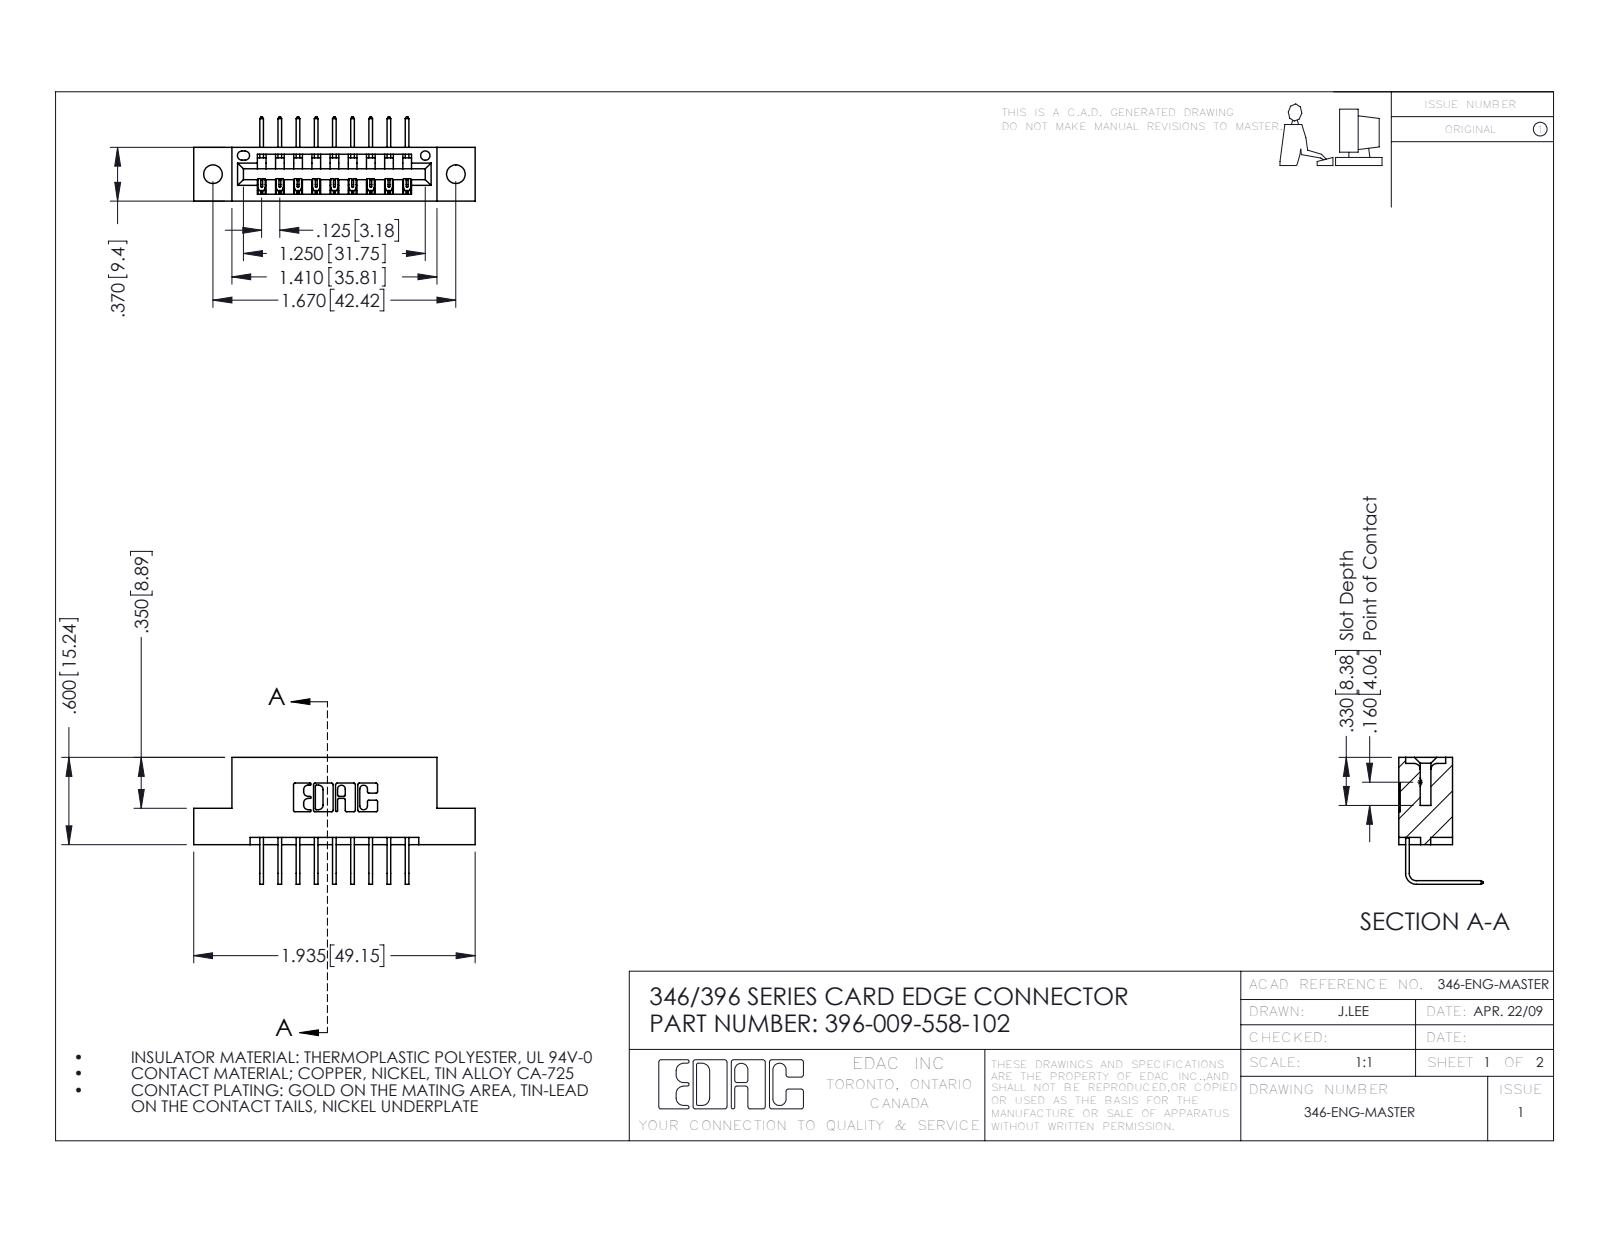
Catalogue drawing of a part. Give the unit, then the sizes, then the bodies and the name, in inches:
Units: inches
Overall size (bounding box): 1.935 × 0.873 × 0.58
Round holes (diameter × count): ⌀0.128 ×2, ⌀0.064 ×1
Partial cylindrical surfaces — rounded edges, fillets, slot ends (radius × count): R0.01 ×22, R0.006 ×18, R0.007 ×6, R0.031 ×6, R0.026 ×3, R0.031 ×2, R0.04 ×2, R0.014 ×1
Main face-to-face distances: 0.25, 0.322, 0.37, 0.048, 0.298, 0.025, 0.148, 0.222, 0.1, 0.174
Hole centre spacings: 0.246, 1.465, 1.67
Volume: 0.273 in³ · Surface area: 7.966 in²
Bodies: 10 solids, 662 faces (454 planar, 208 cylindrical, 0 other)
Part name (STEP PRODUCT): 346 Part_Flush Mounting Lugs - 0.128 Dia; 345-292-001_558 Tail - 2; 396-009-558-102
STEP written by: SolidWorks 2016 (CONFIG_CONTROL_DESIGN)
